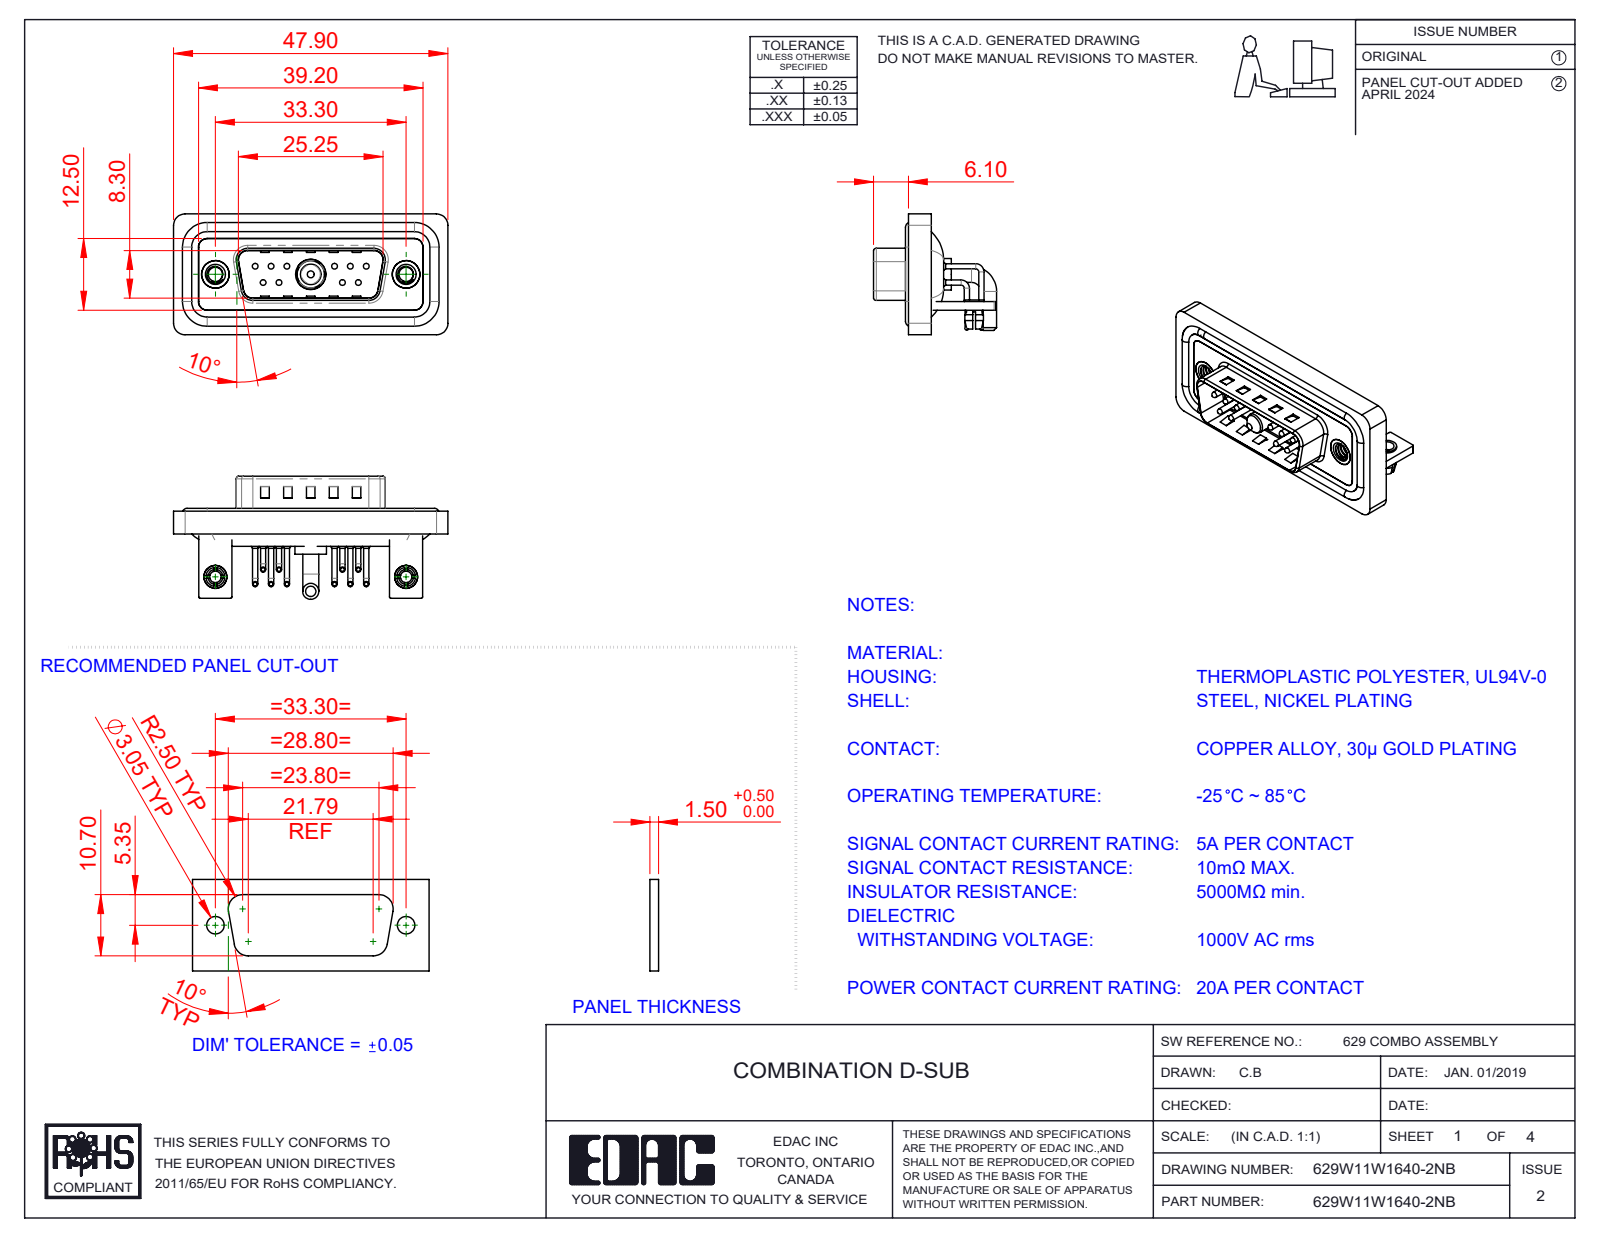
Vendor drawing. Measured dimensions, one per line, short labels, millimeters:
name: 629Combo Shell Rear_15 Contacts; Power Pin_20A RA; 629Combo Stabilizer Bracket; 629Combo Contact Row 1 (+7 more)
written by: SolidWorks 2023 (CONFIG_CONTROL_DESIGN)
unit: mm
bodies: 23 solids, 1733 faces (904 planar, 619 cylindrical, 210 other)
size: 47.9 × 21.5 × 21.1
volume: 5 898 mm³; area: 10 079 mm²
holes: 12× ⌀2, 10× ⌀0.75, 10× ⌀1.6, 4× ⌀2.5, 2× ⌀3.2, 2× ⌀4, 2× ⌀4.8, 2× ⌀5, 1× ⌀4.85, 1× ⌀5.3
bosses: 20× ⌀0.9, 10× ⌀1.5, 10× ⌀1, 10× ⌀0.65, 4× ⌀1.6, 2× ⌀4.9, 2× ⌀4, 2× ⌀3.4
rounds: 21× R2, 18× R1.5, 16× R0.25, 10× R1.01, 9× R0.5, 8× R1.6, 7× R1, 4× R0.6
face distances: 0.4, 0.8, 1.5, 2.9, 2.1, 1.1, 1.6, 1.2, 3.7, 4.1
hole spacings: 3.16, 2.77, 13.85, 11.08, 16.62, 5.03, 5.04, 5.54
